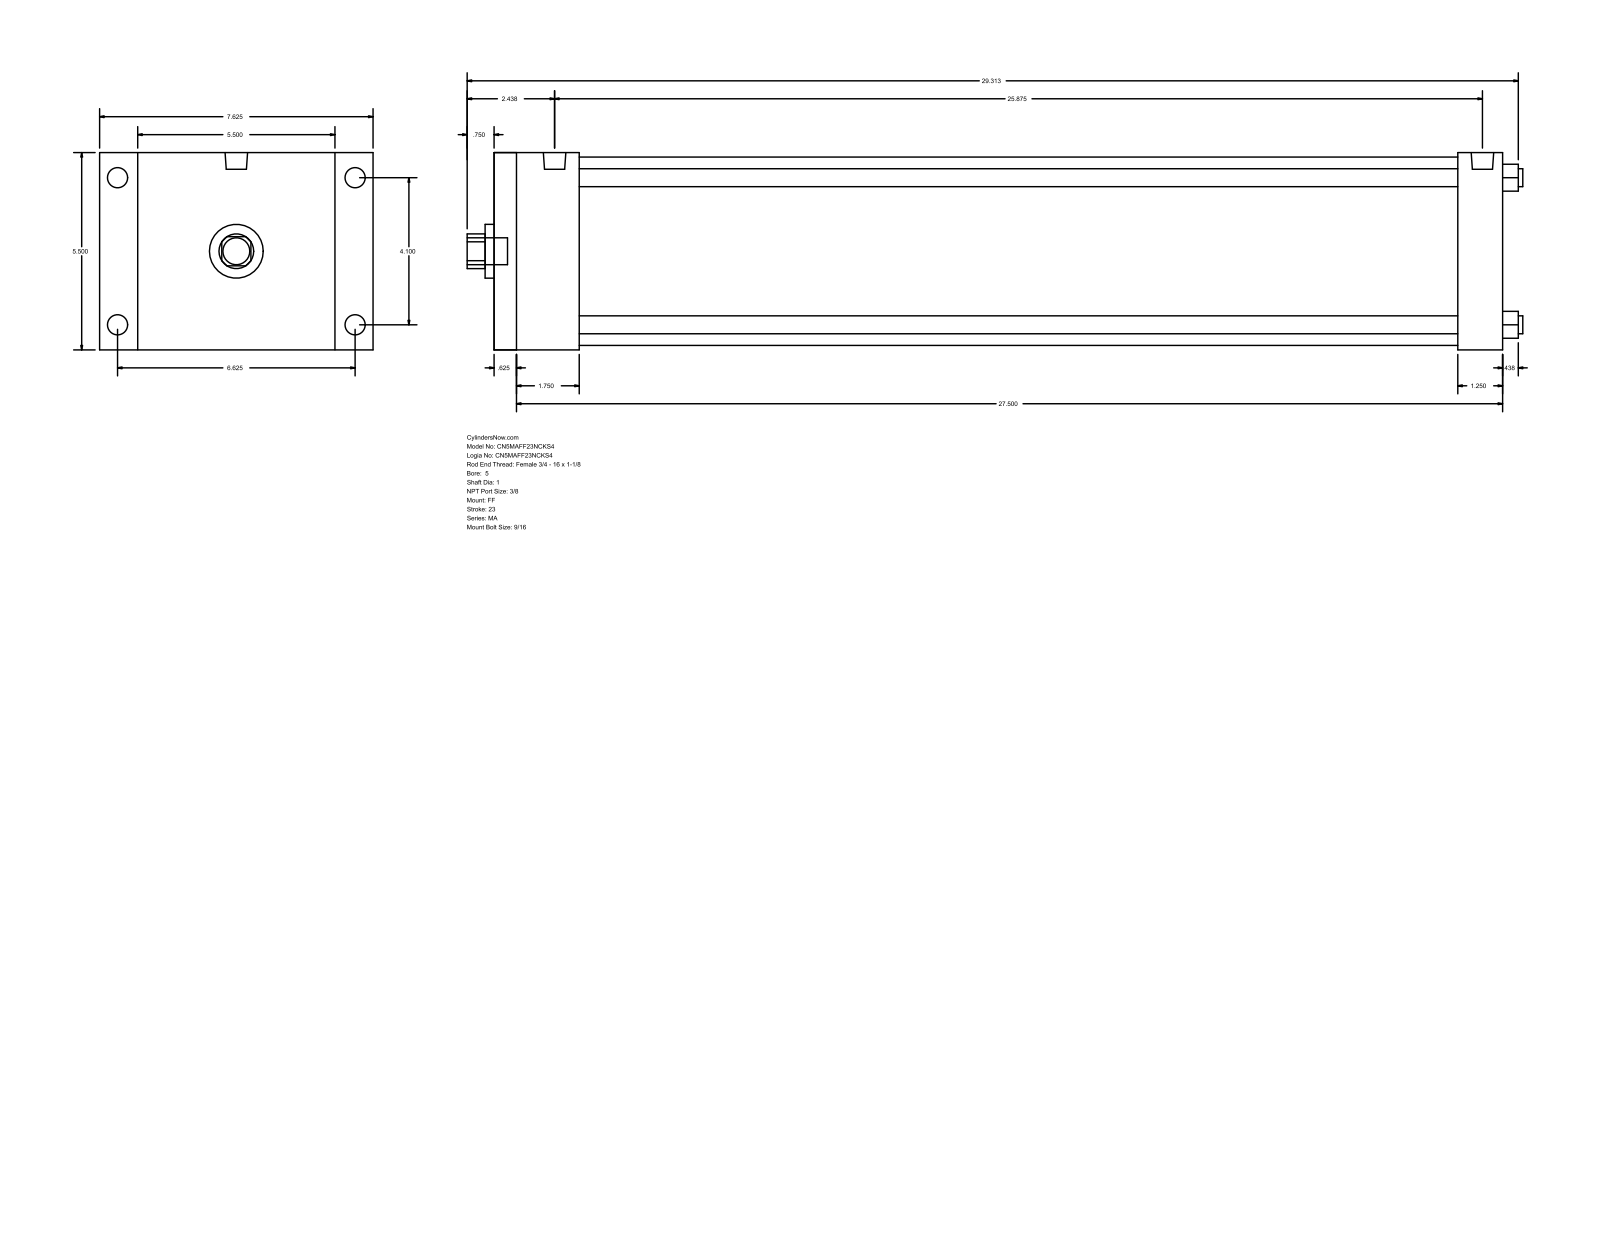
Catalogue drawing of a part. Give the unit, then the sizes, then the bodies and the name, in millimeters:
Units: millimetres
Overall size (bounding box): 747.71 × 193.68 × 139.7
Round holes (diameter × count): ⌀12.7 ×4, ⌀25.4 ×1, ⌀38.1 ×1, ⌀133.35 ×1
Round bosses / shafts (diameter × count): ⌀14.29 ×4, ⌀11.11 ×4, ⌀15.93 ×2, ⌀19.05 ×1
Partial cylindrical surfaces — rounded edges, fillets, slot ends (radius × count): R12.29 ×1
Main face-to-face distances: 139.7, 714.37, 15.87, 698.5, 682.62, 666.75, 31.75, 60.33, 44.46, 622.29
Hole centre spacings: 73.64, 104.14, 147.28
Bodies: 0 solids, 92 faces (64 planar, 28 cylindrical, 0 other)
Part name (STEP PRODUCT): MA_FF__0500_1
STEP written by: GSSL Pune (CONFIG_CONTROL_DESIGN)
